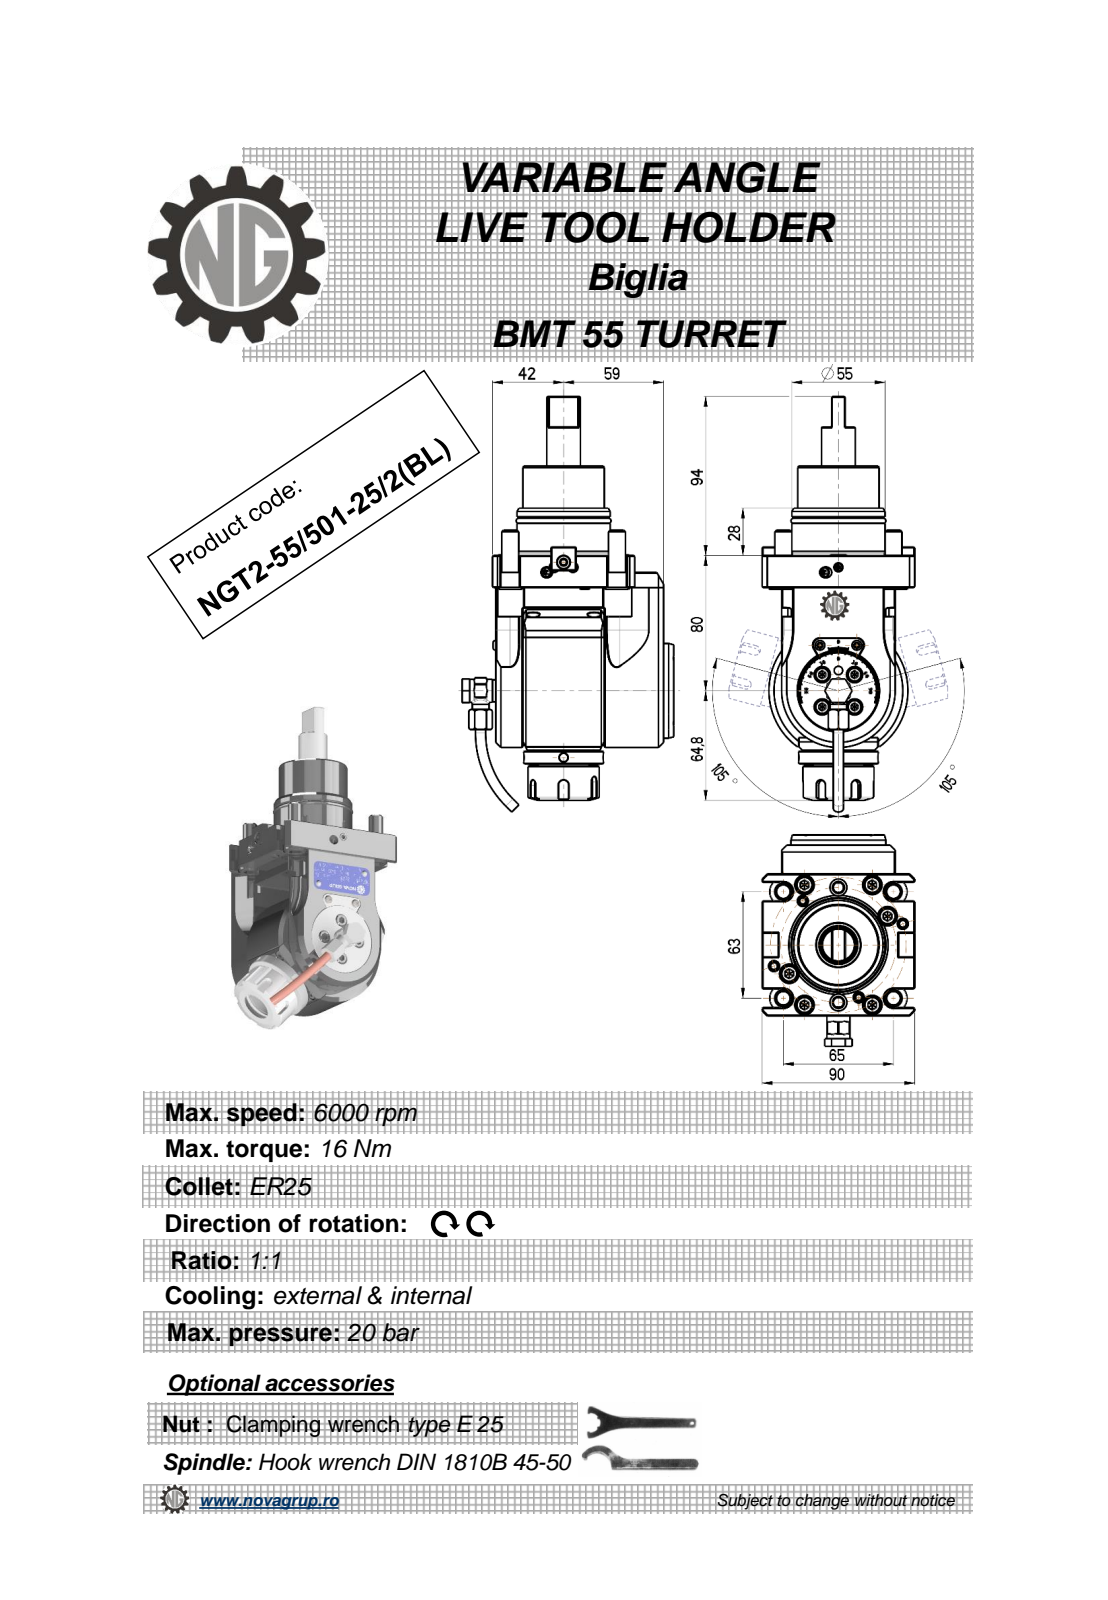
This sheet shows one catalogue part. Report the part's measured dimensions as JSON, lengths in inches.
{"part_name": "NGT2_55_501_25_2_BL", "step_written_by": "PRO/ENGINEER BY PARAMETRIC TECHNOLOGY CORPORATION, 2010280 (CONFIG_CONTROL_DESIGN)", "units": "inches", "bodies": {"solids": 2, "faces": 691, "planar": 301, "cylindrical": 180, "other": 210}, "overall_size": [9.672, 4.917, 3.543], "volume_in3": 55.63, "surface_area_in2": 144, "round_holes": [[0.157, 3], [0.197, 2], [0.236, 2], [0.118, 1], [0.244, 1], [0.354, 1], [0.433, 1], [0.799, 1]], "round_bosses_or_shafts": [[0.394, 6], [0.236, 4], [0.224, 2], [2.205, 1], [2.165, 1], [2.142, 1], [1.969, 1], [1.89, 1]], "partial_cylinders_radius": [[0.013, 20], [0.197, 8], [0.335, 8], [0.118, 5], [0.02, 4], [0.217, 4], [0.315, 4], [0.031, 2]], "face_to_face_distances": [1.22, 2.598, 3.898, 0.079, 0.709, 0.236, 3.307, 1.614, 0.63, 4.134], "hole_center_spacings": [1.339, 0.016, 0.591, 0.606, 1.553, 1.929, 1.945, 2.677]}
